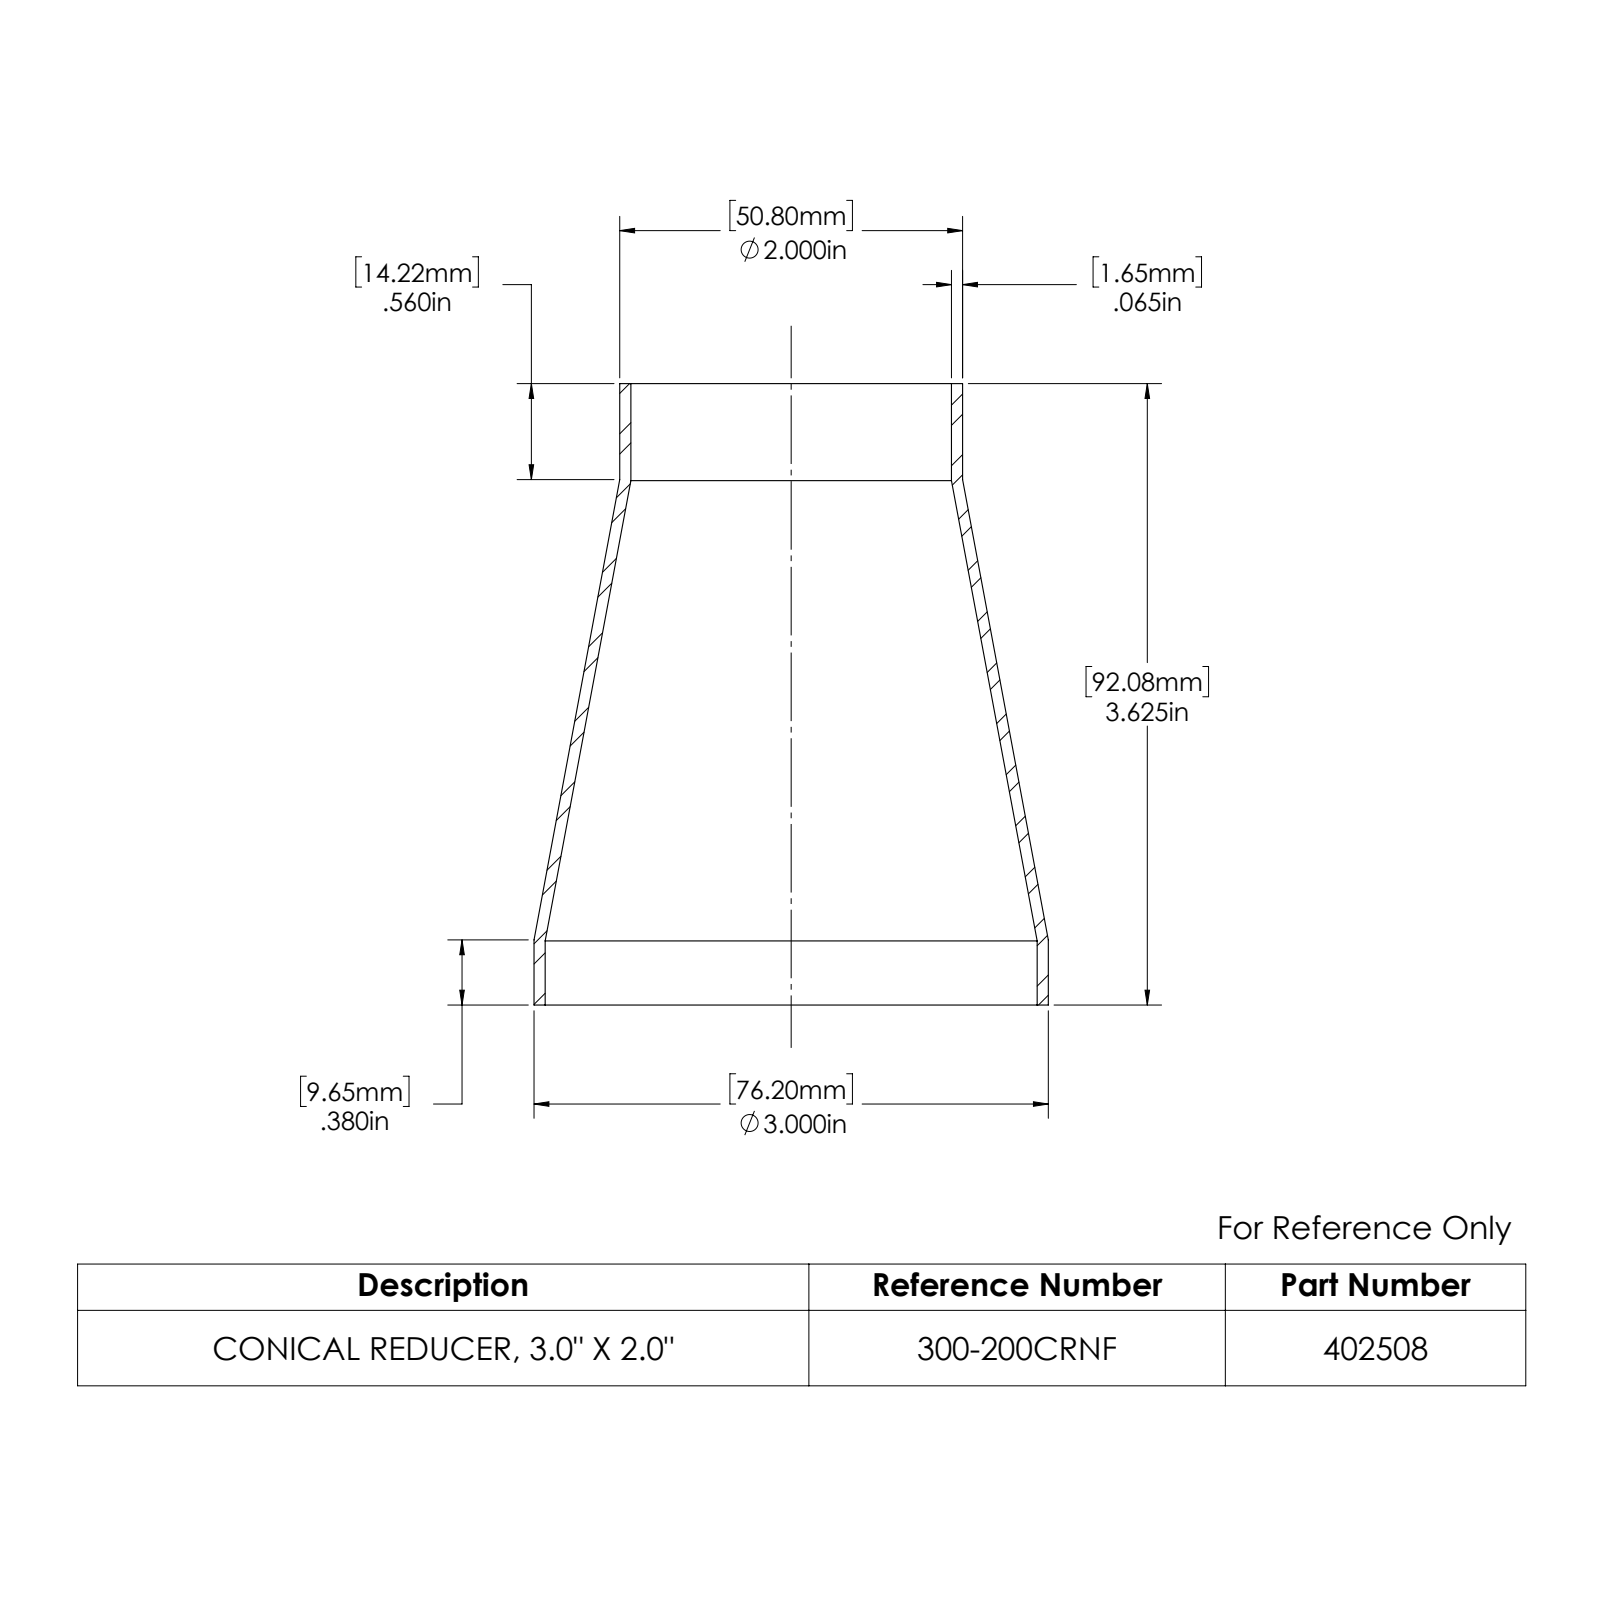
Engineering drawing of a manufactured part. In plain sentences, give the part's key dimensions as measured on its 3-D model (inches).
The part is named "402508". Its 3-D file was written by "SolidWorks 2022 (AUTOMOTIVE_DESIGN)". It is 1 solid with 14 faces: 2 planar, 8 cylindrical and 4 other. Overall it measures 3.625 by 3 by 3 inches. Its volume is 1.806 cubic inches and its surface area 56.58 square inches. Round holes: 1 of diameter 1.87, 1 of diameter 2.87. Round bosses or shafts: 1 of diameter 3, 1 of diameter 2. The main face-to-face distances are 3.625.
